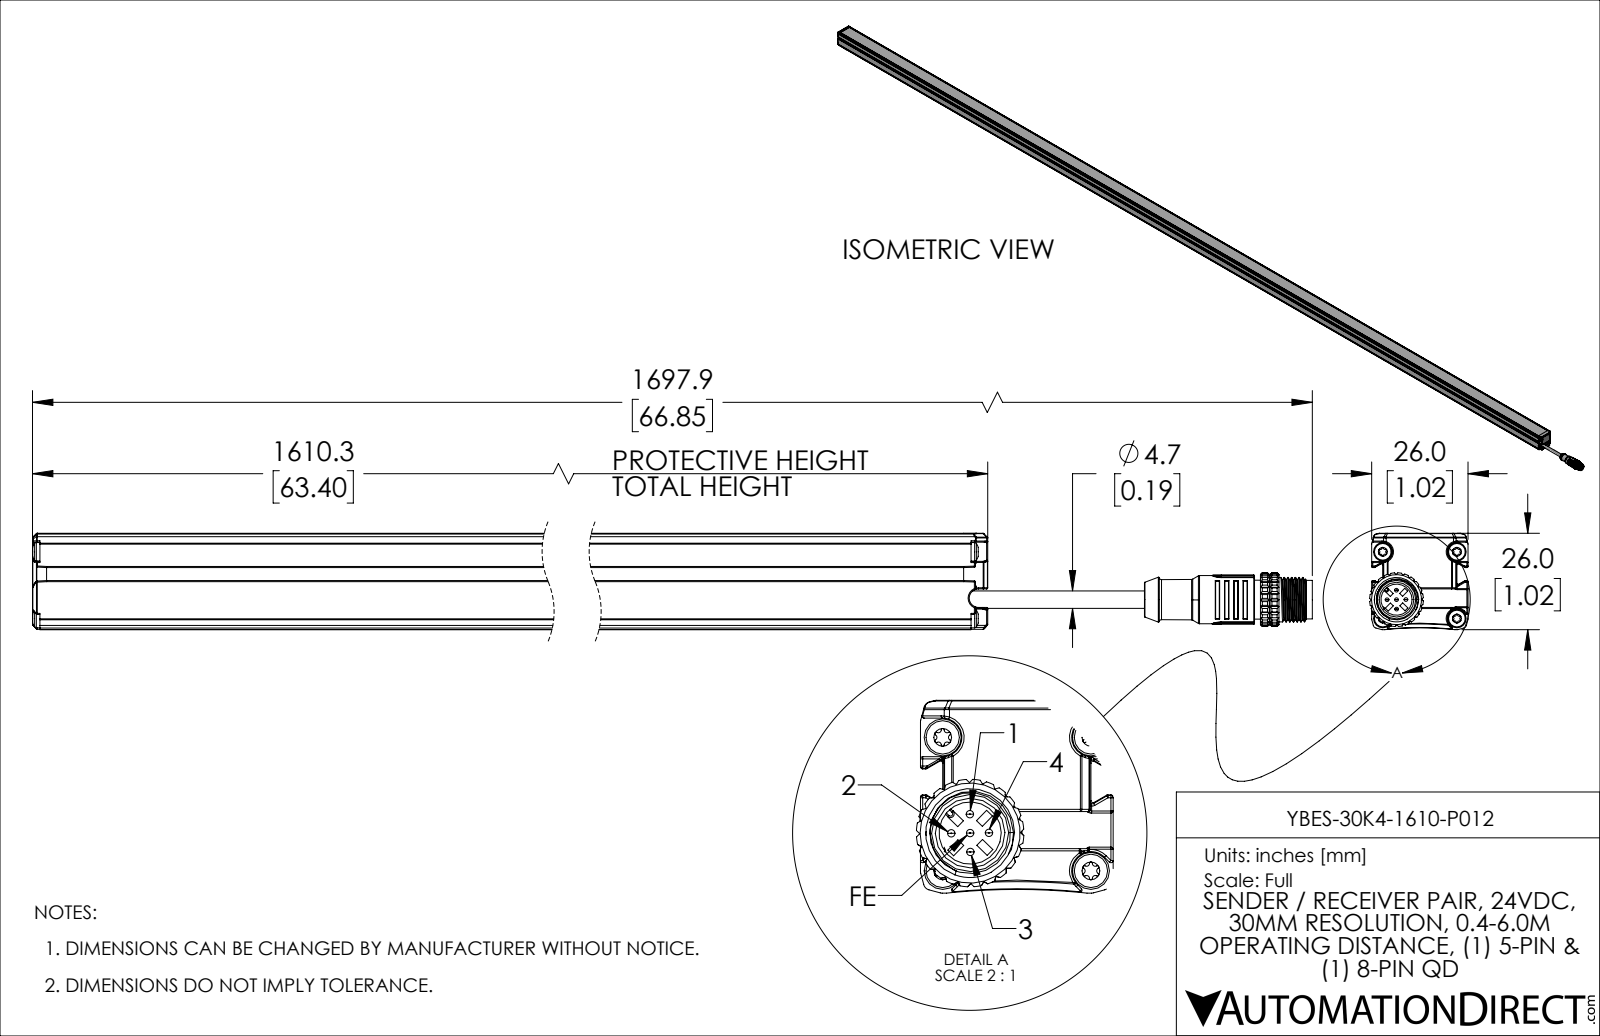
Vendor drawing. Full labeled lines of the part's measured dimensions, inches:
Part name (STEP PRODUCT): YBES-30K4-1610-P012_REV1
STEP written by: SolidWorks 2019 (AUTOMOTIVE_DESIGN)
Units: inches
Bodies: 2 solids, 1743 faces (549 planar, 718 cylindrical, 476 other)
Overall size (bounding box): 66.846 × 1.045 × 1.024
Volume: 22.88 in³ · Surface area: 616.1 in²
Round holes (diameter × count): ⌀0.094 ×4, ⌀0.1 ×4, ⌀0.146 ×4, ⌀0.197 ×4, ⌀0.189 ×1, ⌀0.232 ×1, ⌀0.331 ×1
Round bosses / shafts (diameter × count): ⌀0.039 ×5, ⌀0.126 ×4, ⌀0.098 ×4, ⌀0.051 ×4, ⌀0.059 ×2, ⌀0.531 ×1, ⌀0.512 ×1, ⌀0.472 ×1
Partial cylindrical surfaces — rounded edges, fillets, slot ends (radius × count): R0.008 ×152, R0.012 ×115, R0.008 ×24, R0.015 ×24, R0.039 ×18, R0.016 ×16, R0.006 ×10, R0.02 ×7
Main face-to-face distances: 0.118, 0.059, 0.071, 0.835, 1.024, 0.717, 0.047, 0.906, 0.787, 0.189
Hole centre spacings: 0.709, 0.787, 1.059, 0.248, 0.528, 0.672, 0.819
